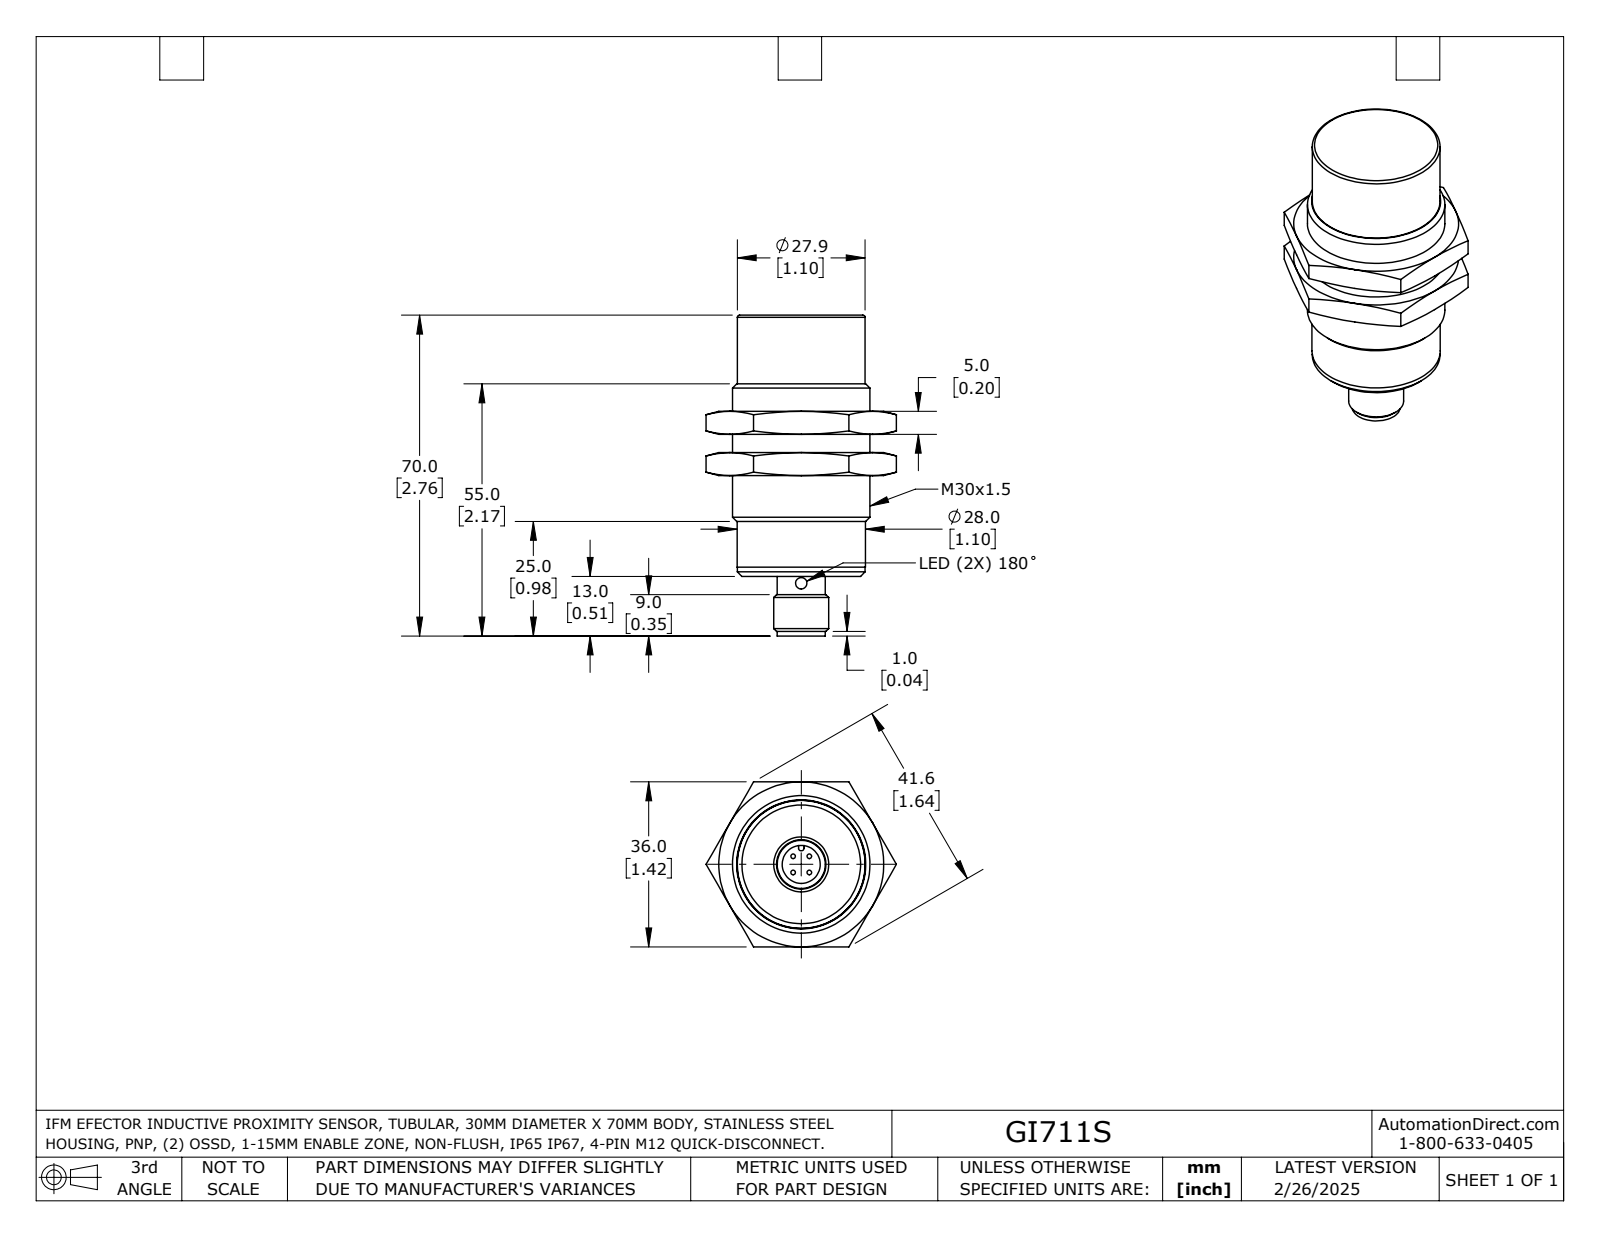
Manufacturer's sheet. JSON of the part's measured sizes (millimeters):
{"part_name": "GI711S", "step_written_by": "SolidWorks 2024 (AUTOMOTIVE_DESIGN)", "units": "millimeters", "bodies": {"solids": 3, "faces": 77, "planar": 28, "cylindrical": 15, "other": 34}, "overall_size": [70, 41.57, 36], "volume_mm3": 43169, "surface_area_mm2": 10996, "round_holes": [[2.5, 1], [8.3, 1], [28.38, 1]], "round_bosses_or_shafts": [[30, 1], [28, 1], [27.9, 1], [12, 1], [10.5, 1]], "partial_cylinders_radius": [[0.6, 1], [4.8, 1]], "face_to_face_distances": [36, 9, 5, 57, 35, 30, 26, 4, 31, 14]}
